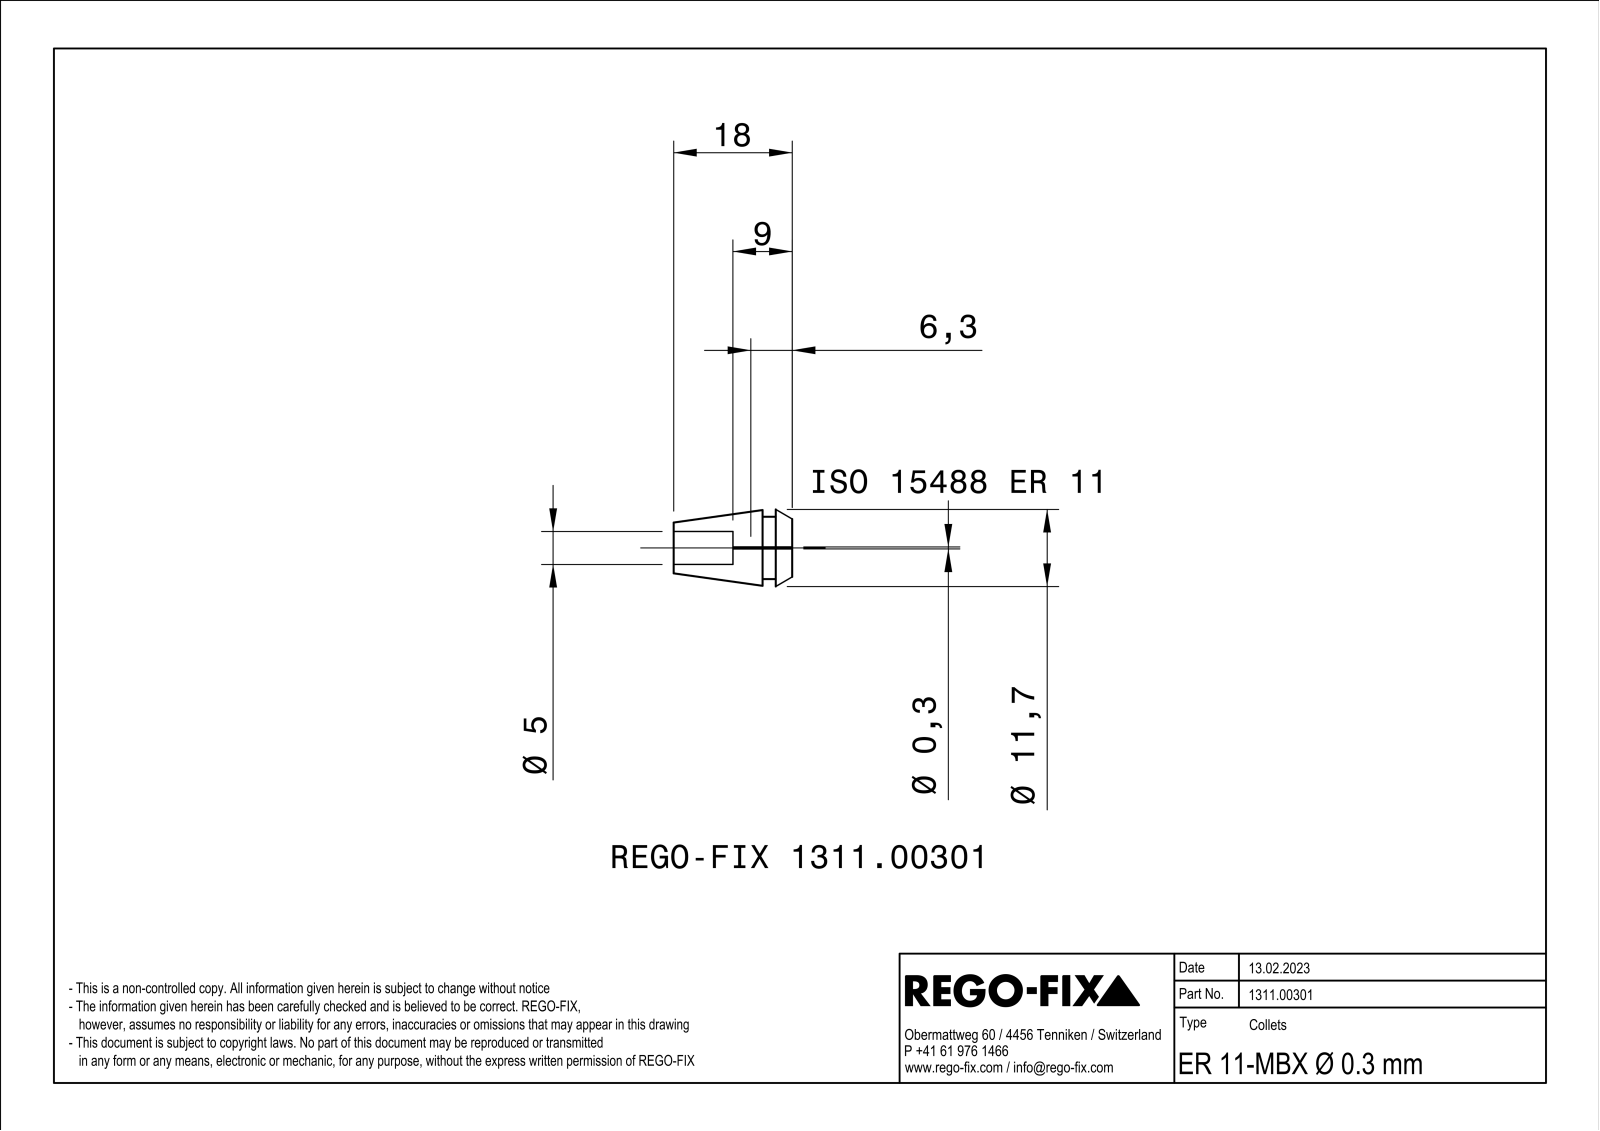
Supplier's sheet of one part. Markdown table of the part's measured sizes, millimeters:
| quantity | value |
| --- | --- |
| part name | NOCUT |
| STEP written by | SIEMENS PLM Software Solid Edge ST10 (AUTOMOTIVE_DESIGN) |
| units | millimeters |
| bodies | 1 solid, 91 faces (26 planar, 19 cylindrical, 46 other) |
| overall size | 18 × 11.41 × 11.39 |
| volume | 995 mm³ |
| surface area | 1 261 mm² |
| round holes (diameter × count) | 1.5 × 3, 5 × 1 |
| round bosses / shafts (diameter × count) | 9.5 × 1 |
| partial cylindrical surfaces (radius × count) | 25 × 3, 0.15 × 1 |
| main face-to-face distances | 0.8, 0.34, 0.46, 4.5, 9, 18, 13.5, 2.5, 2, 15.5 |
| hole center spacings | 1.7, 2.94 |
